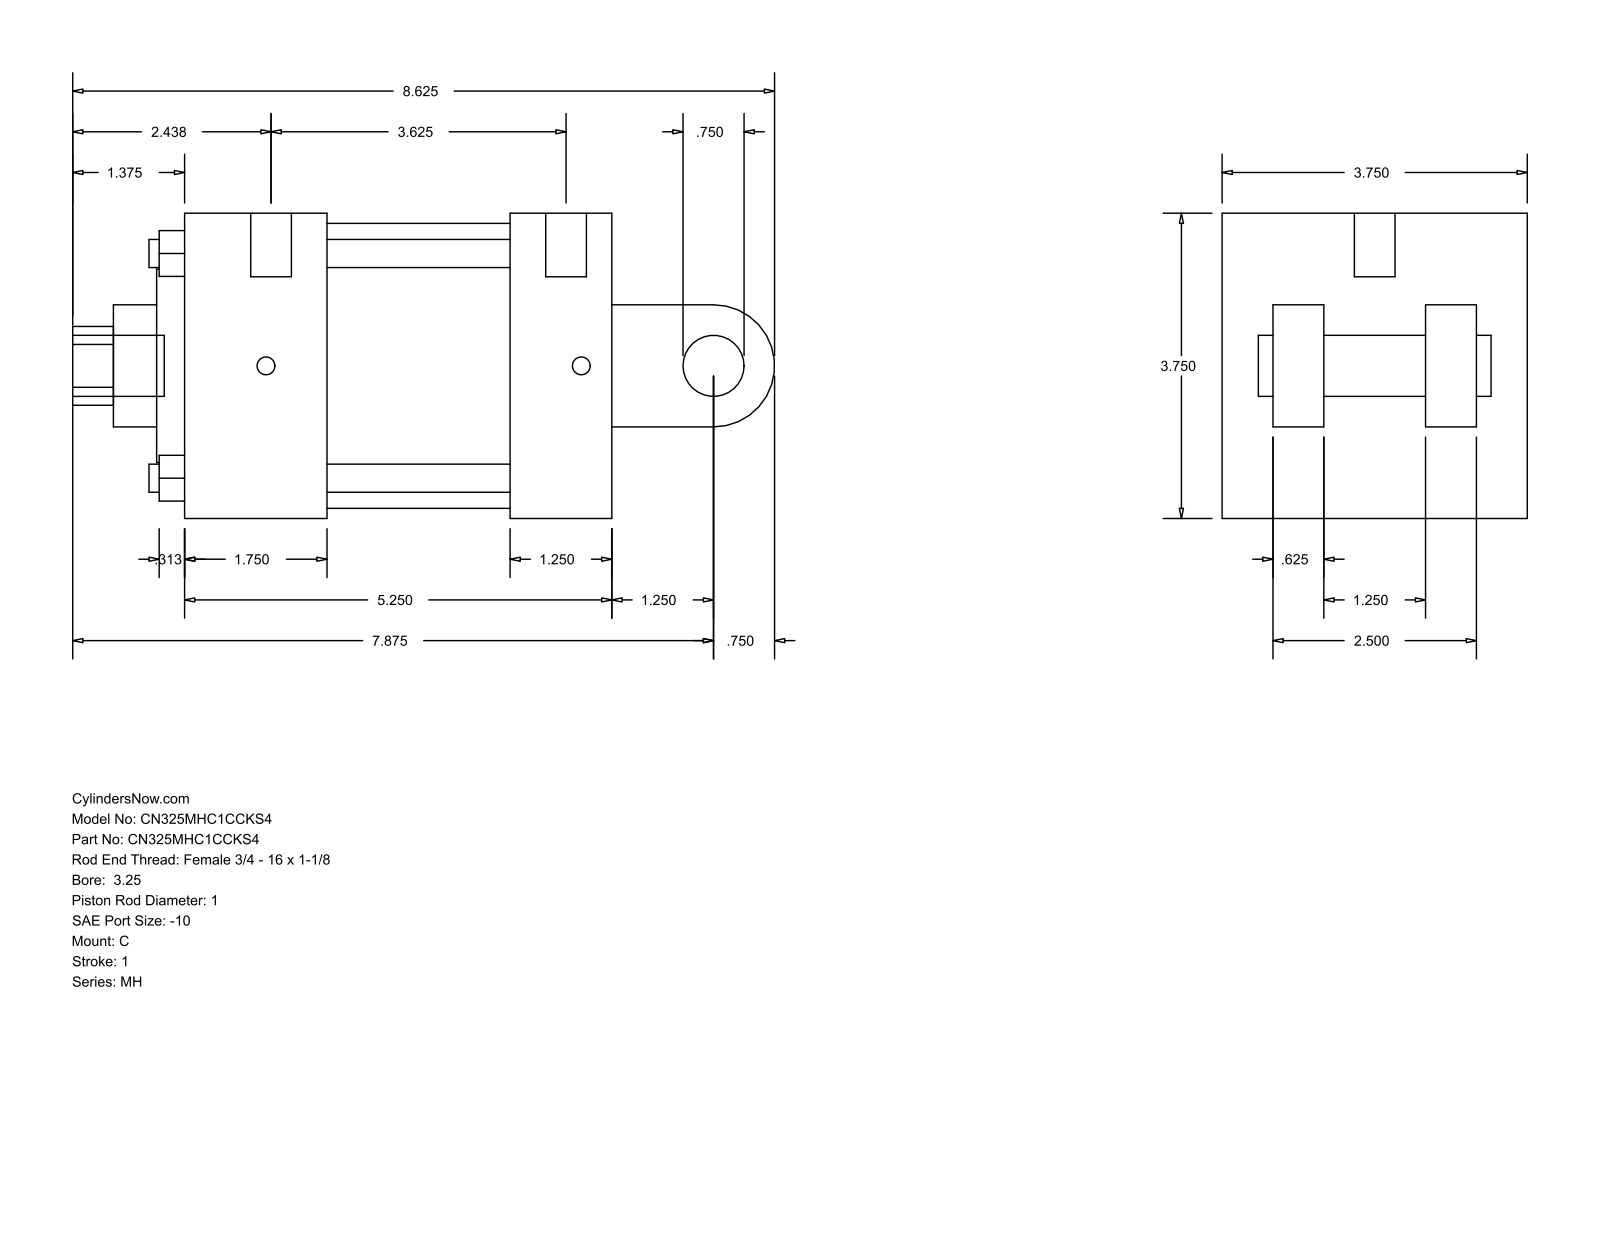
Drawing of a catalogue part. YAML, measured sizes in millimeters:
part_name: "MH_C__0325_1"
step_written_by: "GSSL Pune (CONFIG_CONTROL_DESIGN)"
units: millimeters
bodies: {solids: 0, faces: 101, planar: 71, cylindrical: 30, other: 0}
overall_size: [219.07, 95.25, 95.25]
round_holes:
  - {diameter: 8.76, count: 4}
  - {diameter: 5.56, count: 2}
  - {diameter: 12.7, count: 1}
  - {diameter: 25.4, count: 1}
  - {diameter: 38.1, count: 1}
  - {diameter: 60.33, count: 1}
  - {diameter: 88.9, count: 1}
round_bosses_or_shafts:
  - {diameter: 19.05, count: 2}
  - {diameter: 5.56, count: 2}
  - {diameter: 12.7, count: 1}
partial_cylinders:
  - {radius: 12.29, count: 1}
  - {radius: 19.05, count: 1}
face_to_face_distances: [95.24, 15.87, 133.36, 63.5, 79.37, 31.74, 47.63, 44.46, 101.61, 57.15]
hole_center_spacings: [49.57, 70.1, 99.14, 4.76]
